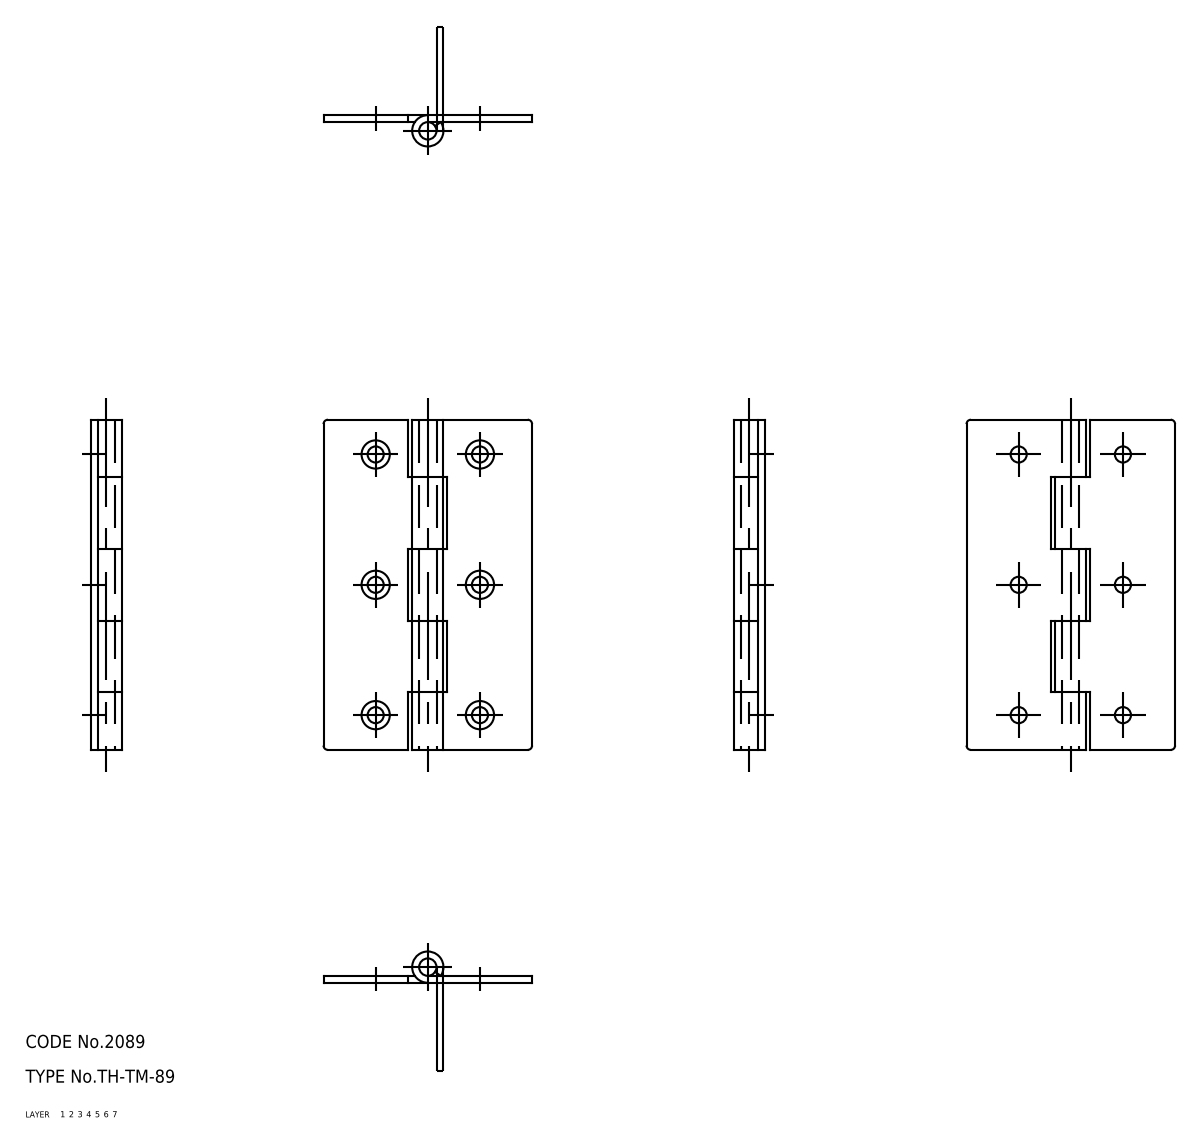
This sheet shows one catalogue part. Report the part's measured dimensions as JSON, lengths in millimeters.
{"part_name": "shaft; hinge piece_B; hinge piece_A; TH_TM_89_26578_36", "step_written_by": "CADfix (AUTOMOTIVE_DESIGN)", "units": "millimeters", "bodies": {"solids": 3, "faces": 70, "planar": 0, "cylindrical": 0, "other": 70}, "overall_size": [76, 48, 7.2], "volume_mm3": 7856, "surface_area_mm2": 10699}
